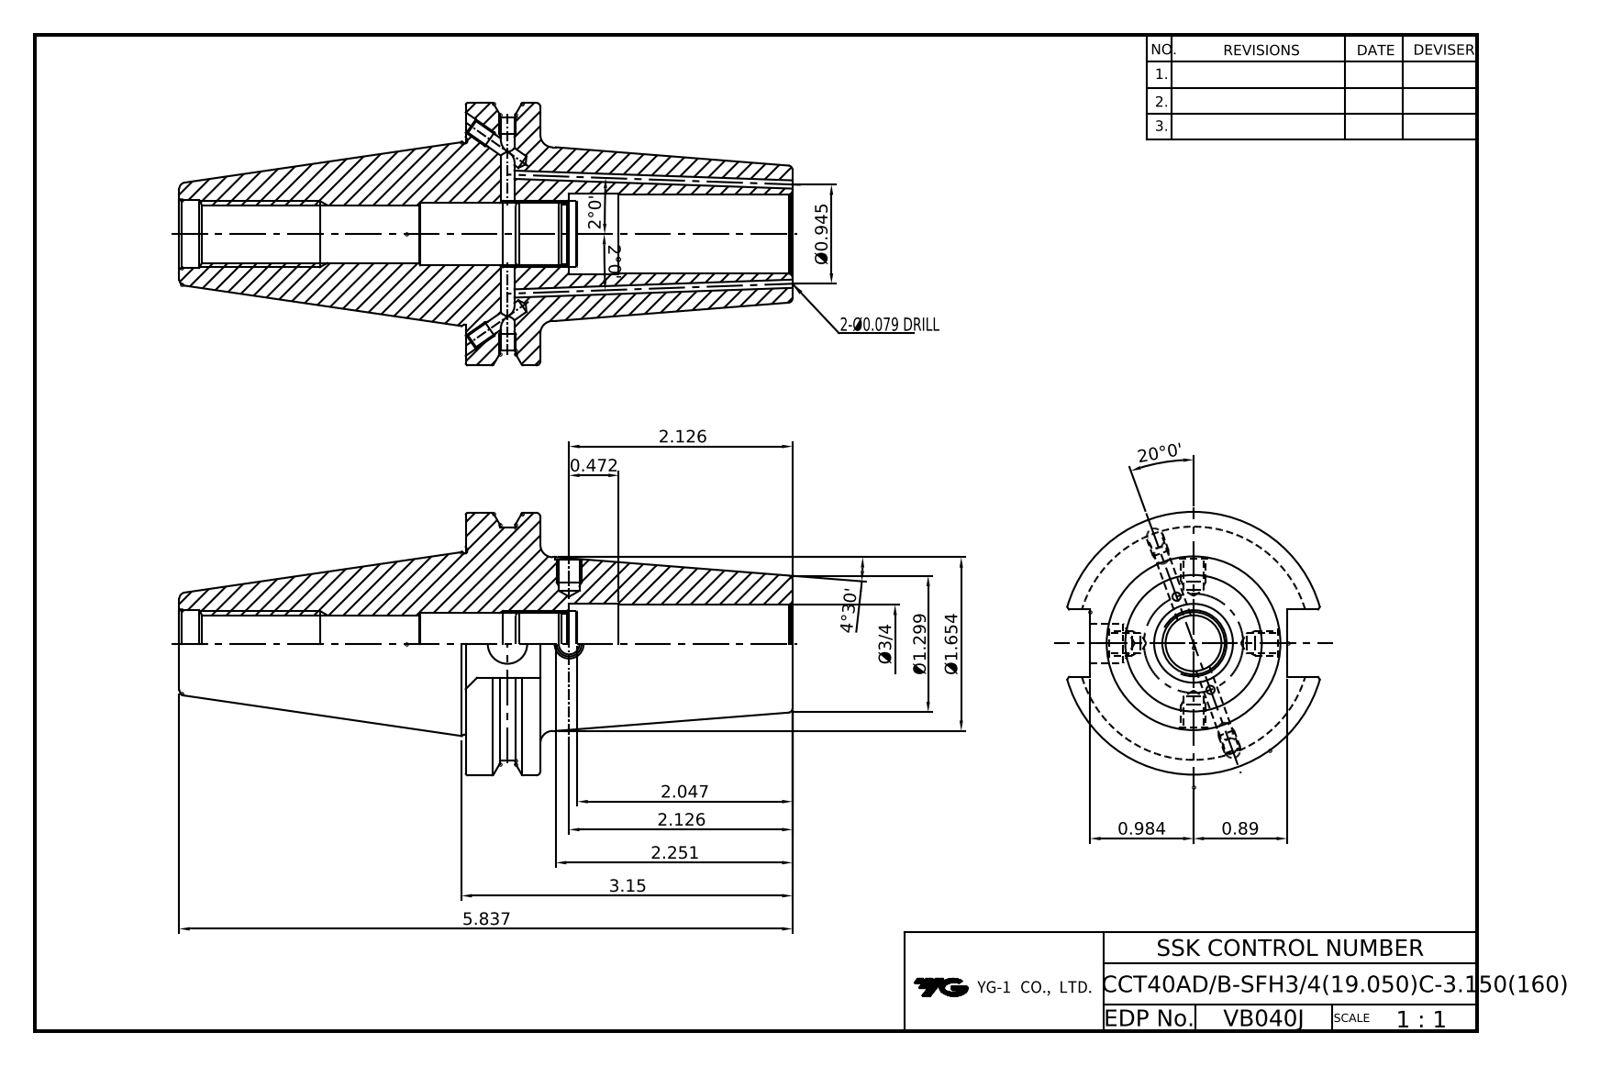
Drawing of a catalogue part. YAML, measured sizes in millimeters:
part_name: "LO-CCT40ADB-SFH3_4C-3_15"
step_written_by: "CREO PARAMETRIC BY PTC INC, 2018100 (CONFIG_CONTROL_DESIGN)"
units: millimeters
bodies: {solids: 1, faces: 145, planar: 49, cylindrical: 62, other: 34}
overall_size: [148.25, 63.5, 61]
volume: 153832
surface_area: 33704
round_holes:
  - {diameter: 4, count: 7}
  - {diameter: 3.4, count: 3}
  - {diameter: 9.53, count: 1}
  - {diameter: 13.5, count: 1}
  - {diameter: 14, count: 1}
  - {diameter: 15, count: 1}
  - {diameter: 15.88, count: 1}
  - {diameter: 16, count: 1}
  - {diameter: 16.3, count: 1}
  - {diameter: 19.05, count: 1}
  - {diameter: 19.65, count: 1}
round_bosses_or_shafts:
  - {diameter: 63.5, count: 1}
  - {diameter: 43.8, count: 1}
  - {diameter: 42, count: 1}
partial_cylinders:
  - {radius: 28.15, count: 1}
face_to_face_distances: [18.05, 79, 60.95, 47.6, 69.25, 87.3, 148.25, 16.38, 94.25, 25]
